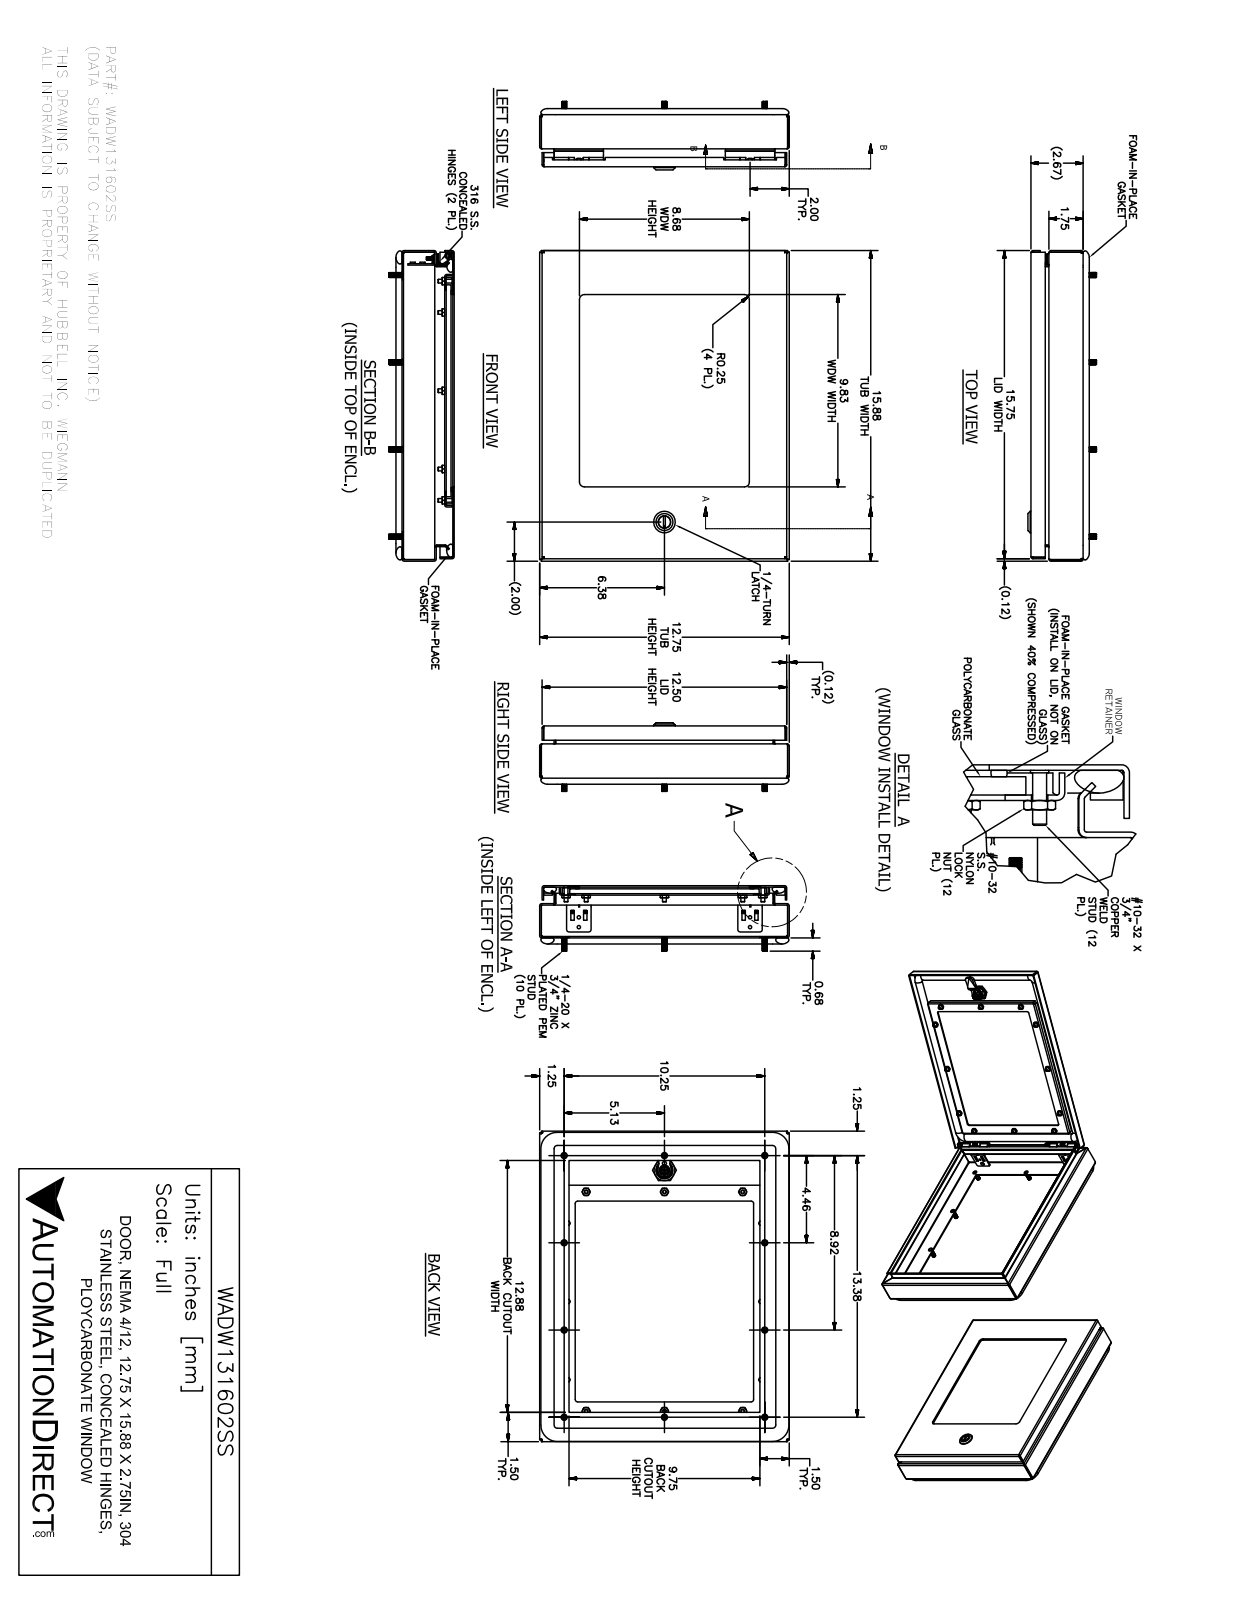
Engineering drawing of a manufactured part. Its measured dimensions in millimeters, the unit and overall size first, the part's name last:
Units: millimetres
Overall size (bounding box): 403.2 × 323.9 × 88.9
Round holes (diameter × count): ⌀4 ×14, ⌀7.1 ×12, ⌀6.3 ×9, ⌀2.4 ×4, ⌀3.9 ×4, ⌀4.2 ×4, ⌀4.4 ×4, ⌀4.8 ×4, ⌀4.7 ×1, ⌀5 ×1, ⌀8 ×1, ⌀10 ×1
Round bosses / shafts (diameter × count): ⌀6.4 ×20, ⌀4.8 ×12, ⌀9.1 ×4, ⌀8.1 ×4, ⌀6.5 ×4, ⌀4.2 ×4, ⌀3.3 ×4, ⌀28 ×1
Partial cylindrical surfaces — rounded edges, fillets, slot ends (radius × count): R0.8 ×34, R0.3 ×30, R1.3 ×26, R2.7 ×24, R3.2 ×20, R0.4 ×18, R0.5 ×13, R0.8 ×8
Main face-to-face distances: 1.9, 10.4, 8.6, 65.9, 6.4, 2.2, 4.1, 55.4, 42.6, 61.8
Hole centre spacings: 101.6, 113.2, 283.9, 222.1, 172.1, 203.2, 226.5, 248.3
Volume: 1 305 000 mm³ · Surface area: 857 400 mm²
Bodies: 65 solids, 1951 faces (724 planar, 625 cylindrical, 602 other)
Part name (STEP PRODUCT): WADW131602SS
STEP written by: SolidWorks 2017 (AUTOMOTIVE_DESIGN)
